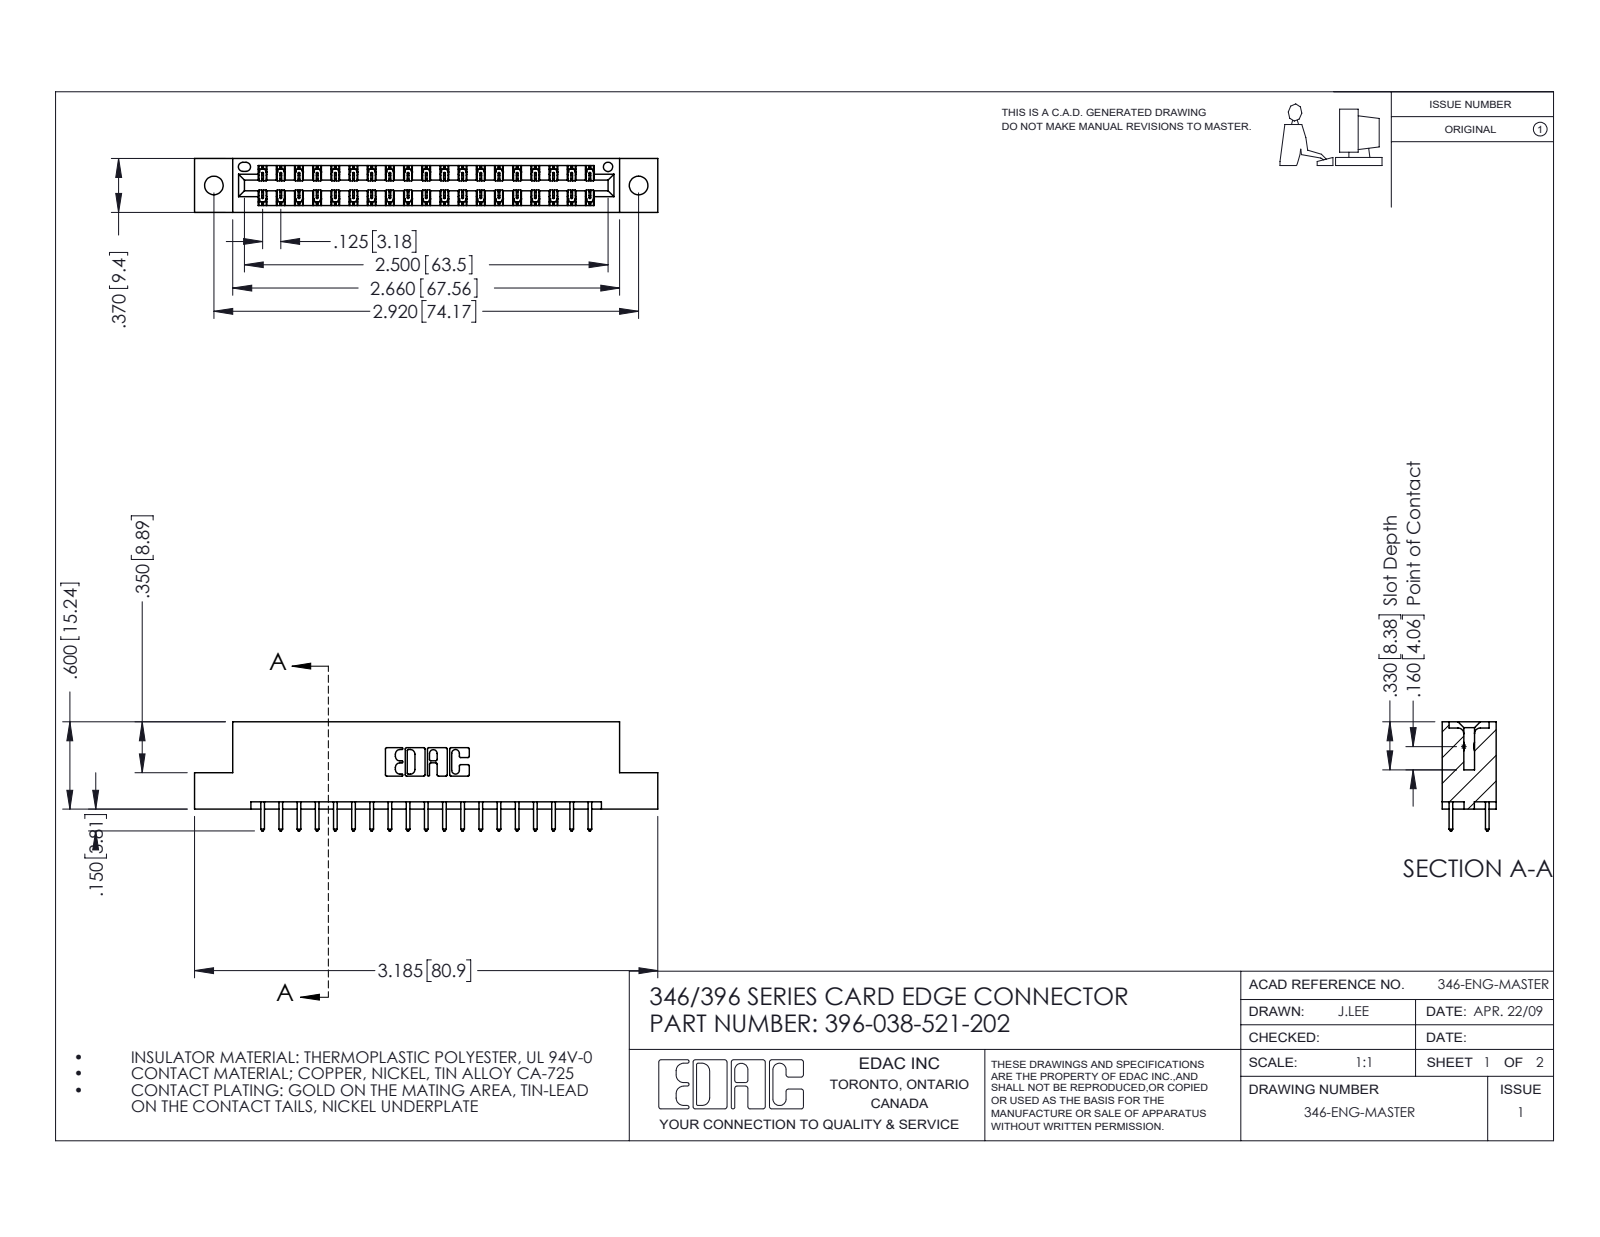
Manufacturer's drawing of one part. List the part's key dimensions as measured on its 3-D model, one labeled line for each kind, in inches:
Part name (STEP PRODUCT): 345-292-001_345-293-121; 396-038-521-202; 346 Part_Flush Mounting Lugs - 0.128 Dia
STEP written by: SolidWorks 2016 (CONFIG_CONTROL_DESIGN)
Units: inches
Bodies: 39 solids, 2098 faces (1406 planar, 692 cylindrical, 0 other)
Overall size (bounding box): 3.185 × 0.75 × 0.37
Volume: 0.467 in³ · Surface area: 15.18 in²
Round holes (diameter × count): ⌀0.128 ×2, ⌀0.064 ×1
Partial cylindrical surfaces — rounded edges, fillets, slot ends (radius × count): R0.006 ×57, R0.01 ×38, R0.01 ×22, R0.007 ×6, R0.031 ×6, R0.026 ×3, R0.014 ×2, R0.022 ×2
Main face-to-face distances: 0.048, 0.322, 0.25, 0.37, 0.072, 0.298, 0.025, 0.275, 0.148, 0.222
Hole centre spacings: 0.246, 2.713, 2.92
